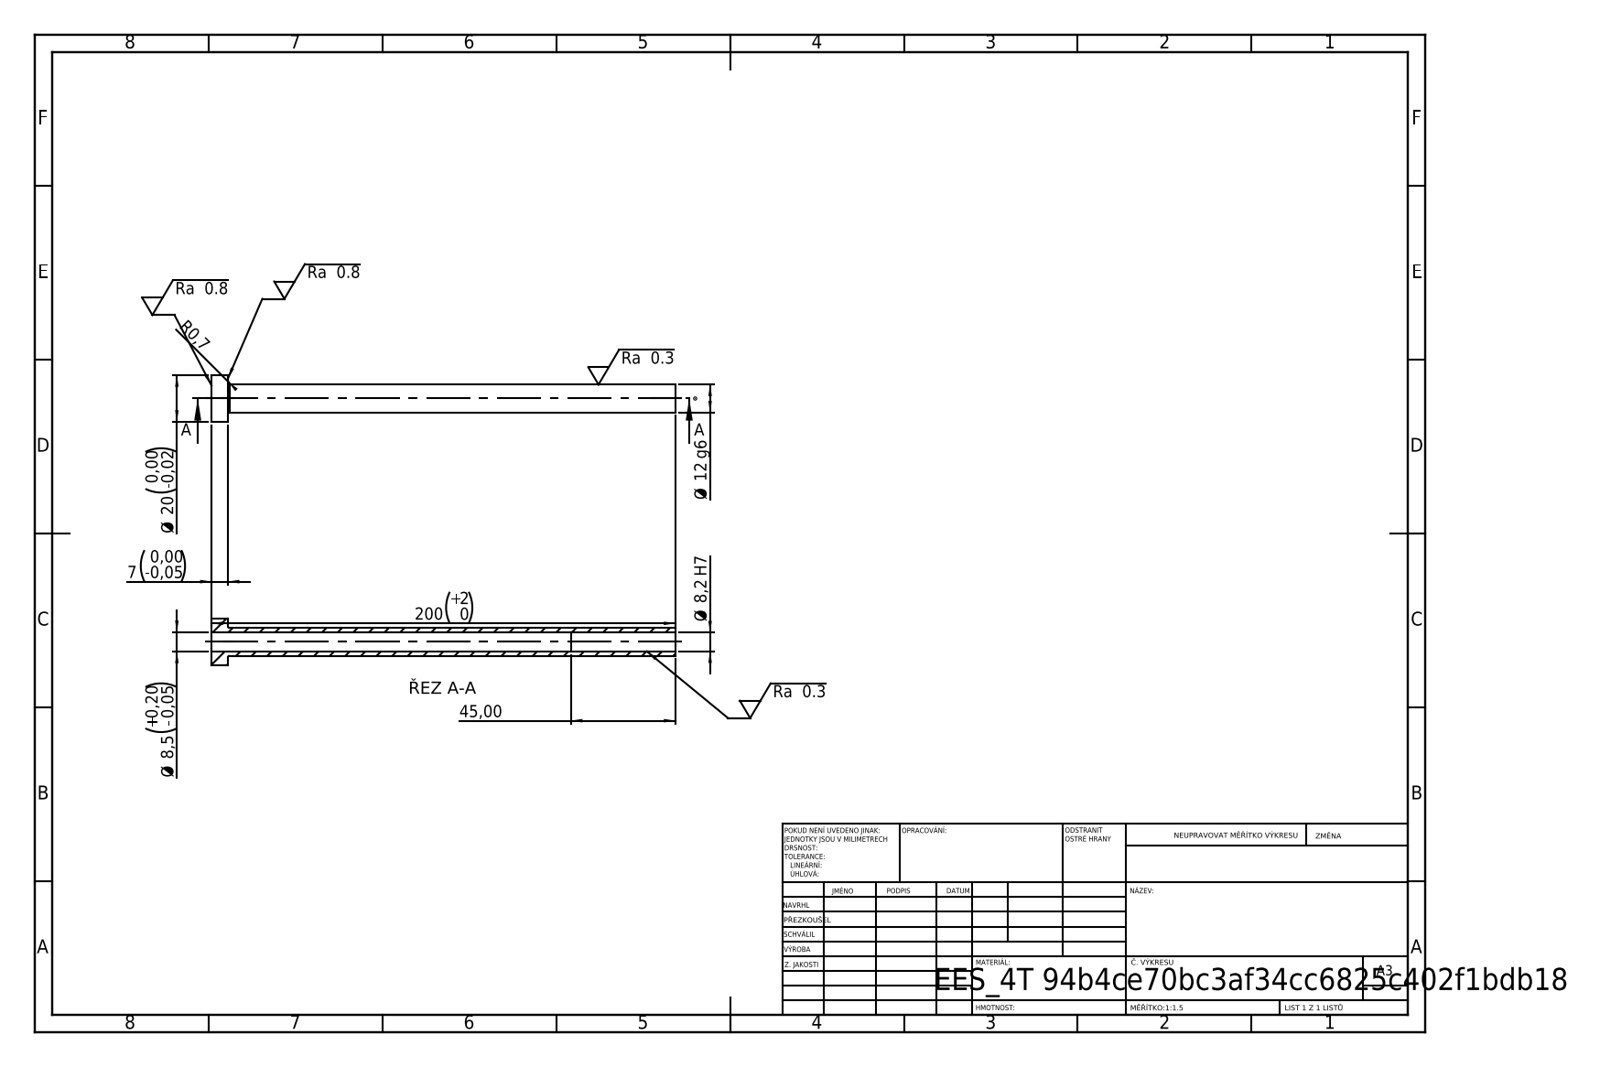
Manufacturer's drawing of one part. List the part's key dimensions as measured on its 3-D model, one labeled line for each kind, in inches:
STEP written by: SolidWorks 2019 (CONFIG_CONTROL_DESIGN)
Units: inches
Bodies: 1 solid, 14 faces (4 planar, 8 cylindrical, 2 other)
Overall size (bounding box): 7.874 × 0.787 × 0.787
Volume: 0.785 in³ · Surface area: 20.97 in²
Round holes (diameter × count): ⌀0.323 ×1, ⌀0.335 ×1
Round bosses / shafts (diameter × count): ⌀0.787 ×1, ⌀0.472 ×1
Main face-to-face distances: 0.276, 7.874, 7.598, 6.102, 5.827, 1.772
